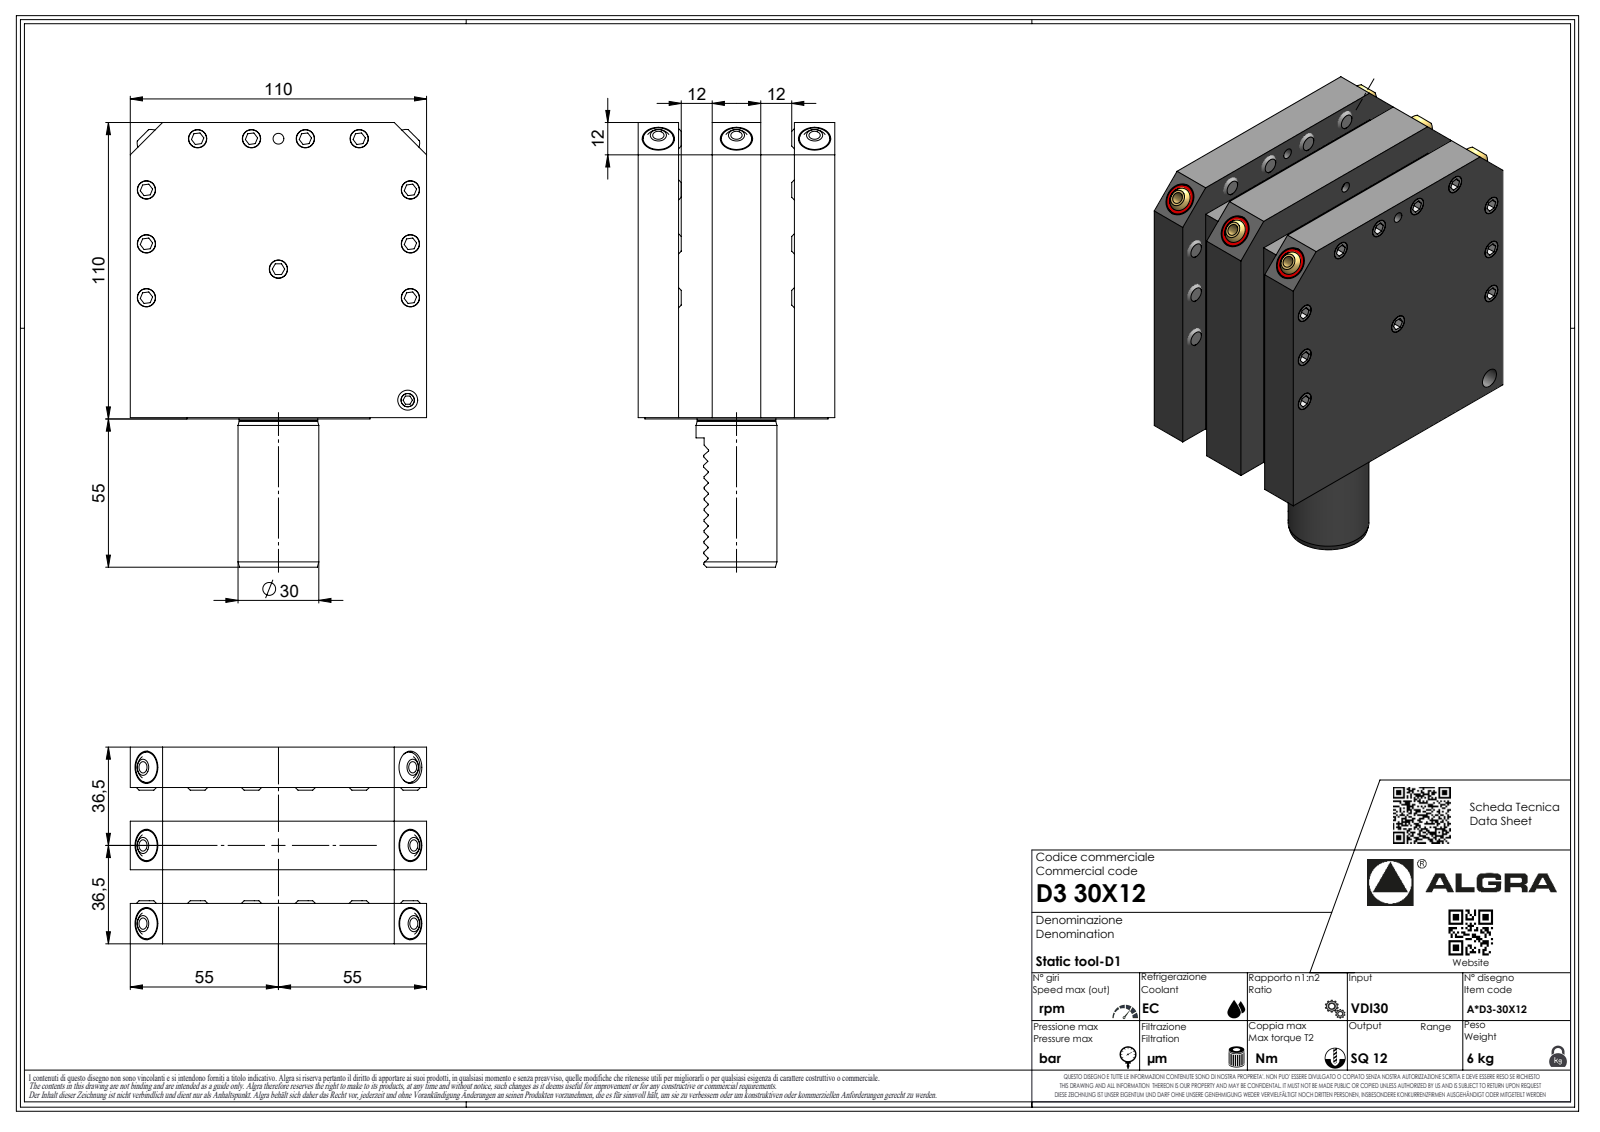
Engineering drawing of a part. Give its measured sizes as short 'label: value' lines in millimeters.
name: D330X12
written by: SolidWorks 2023 (AUTOMOTIVE_DESIGN)
unit: mm
bodies: 1 solid, 377 faces (251 planar, 40 cylindrical, 86 other)
size: 165 × 110 × 73
volume: 819 911 mm³; area: 73 253 mm²
holes: 1× ⌀2.1
bosses: 1× ⌀68, 1× ⌀30, 1× ⌀29.1, 1× ⌀6.37, 1× ⌀1.7
rounds: 7× R0.33, 7× R0.52, 7× R3.7, 3× R0.3, 2× R0.27, 1× R0.21, 1× R0.24, 1× R0.26
face distances: 73, 12, 110, 27.5, 45.5, 98, 15, 58, 12.5, 30.5
